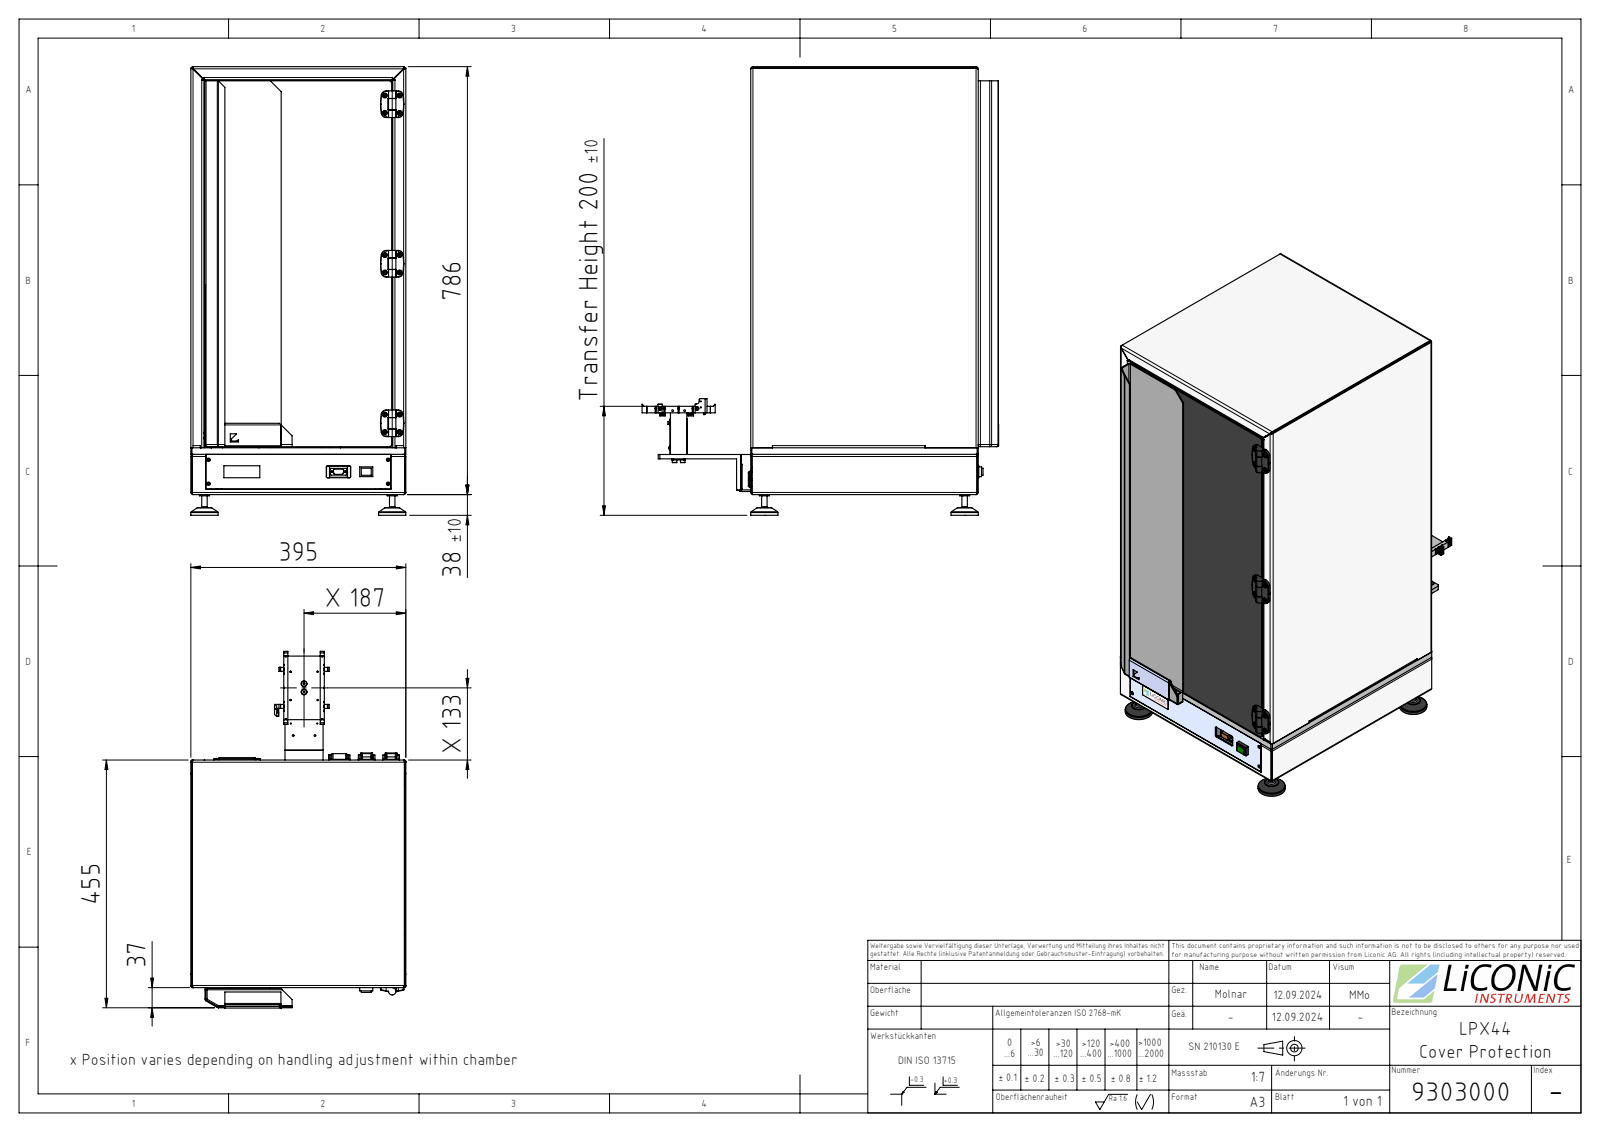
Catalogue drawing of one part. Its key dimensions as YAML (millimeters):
part_name: "9303000"
step_written_by: "SolidWorks 2022 (AUTOMOTIVE_DESIGN)"
units: millimeters
bodies: {solids: 52, faces: 4385, planar: 2380, cylindrical: 1848, other: 157}
overall_size: [824, 655.19, 395.01]
volume: 9020000
surface_area: 5316000
round_holes:
  - {diameter: 4, count: 96}
  - {diameter: 3.3, count: 45}
  - {diameter: 2.5, count: 33}
  - {diameter: 4.2, count: 31}
  - {diameter: 4.5, count: 26}
  - {diameter: 8, count: 19}
  - {diameter: 6, count: 14}
  - {diameter: 5, count: 13}
  - {diameter: 9, count: 12}
  - {diameter: 3.4, count: 10}
  - {diameter: 5.3, count: 10}
  - {diameter: 5.5, count: 10}
round_bosses_or_shafts:
  - {diameter: 4, count: 6}
  - {diameter: 50.01, count: 4}
  - {diameter: 10, count: 4}
  - {diameter: 1.5, count: 3}
  - {diameter: 15.5, count: 1}
  - {diameter: 14.5, count: 1}
  - {diameter: 13.5, count: 1}
partial_cylinders:
  - {radius: 2, count: 497}
  - {radius: 2.5, count: 112}
  - {radius: 1, count: 94}
  - {radius: 4, count: 50}
  - {radius: 1.5, count: 24}
  - {radius: 6, count: 16}
  - {radius: 10, count: 15}
  - {radius: 3, count: 14}
face_to_face_distances: [2, 393, 418, 395, 416, 391, 784, 1, 12, 413]
hole_center_spacings: [23, 46, 69, 92, 115, 138, 161, 184]
